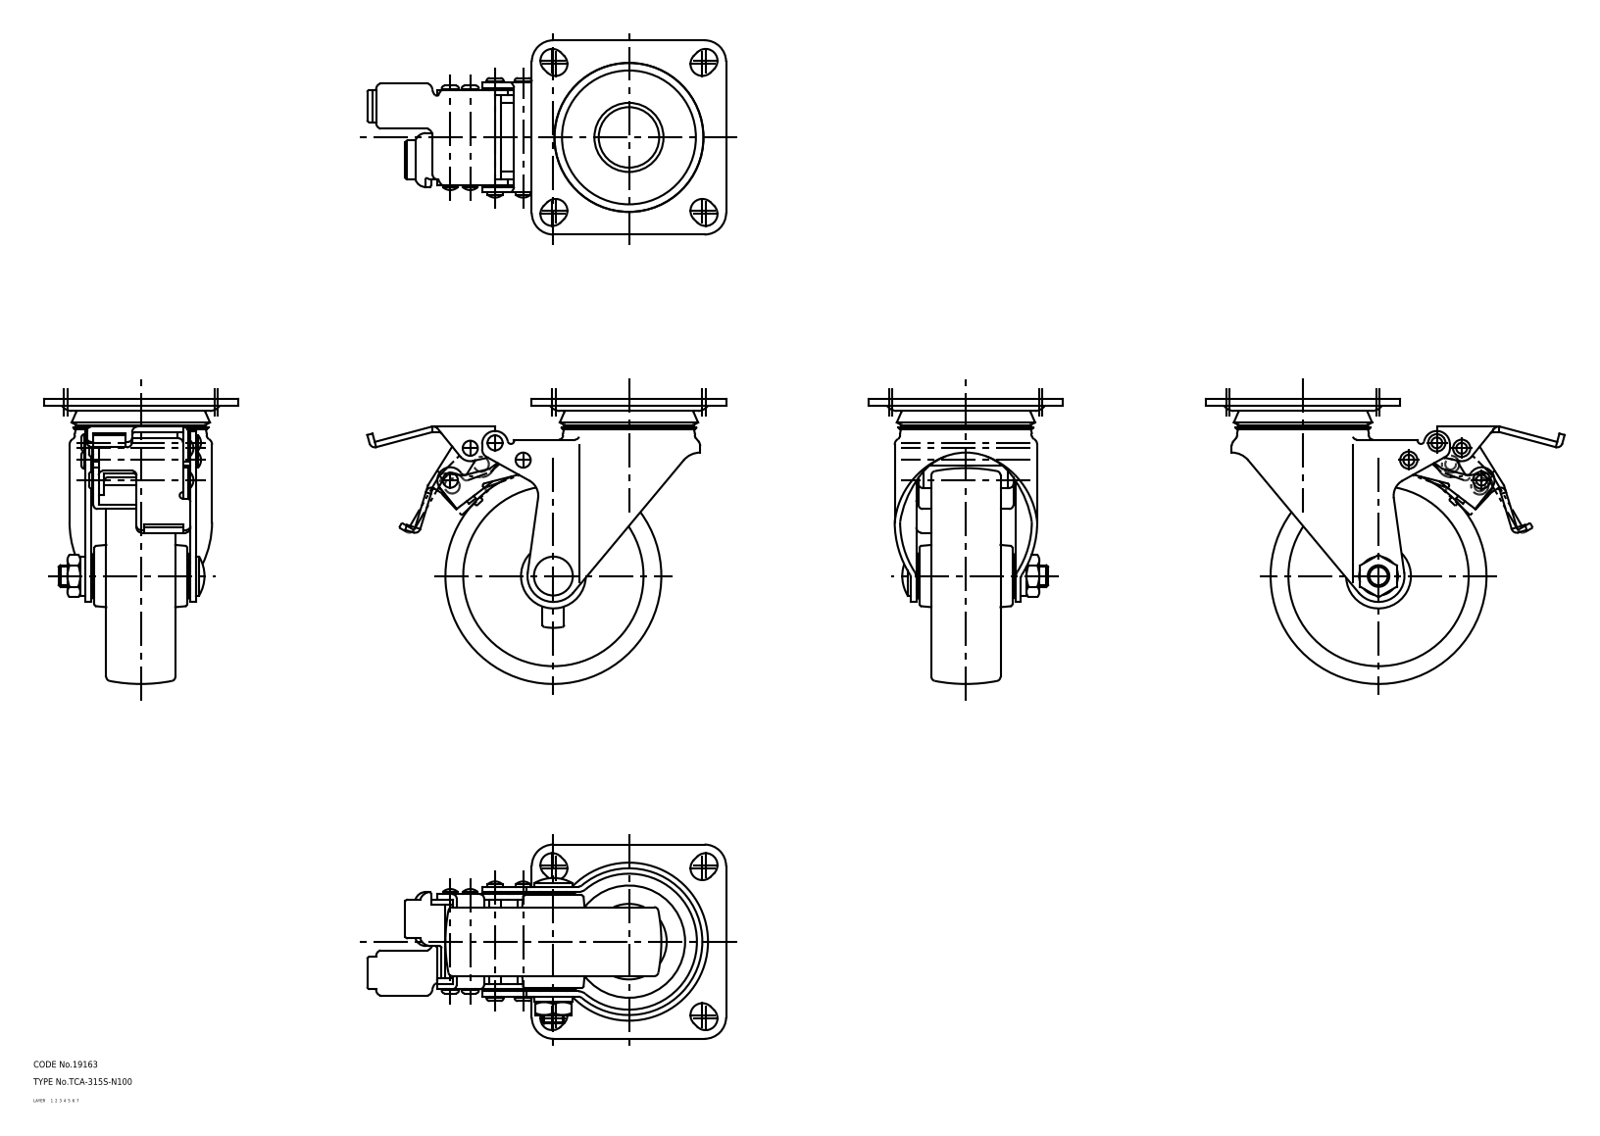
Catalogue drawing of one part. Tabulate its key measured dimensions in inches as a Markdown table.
| quantity | value |
| --- | --- |
| part name | 67138004; 67138017; 67138030; 67138043 (+2 more) |
| STEP written by | CADfix (AUTOMOTIVE_DESIGN) |
| units | inches |
| bodies | 6 solids, 462 faces (0 planar, 0 cylindrical, 462 other) |
| overall size | 6.543 × 5.197 × 3.543 |
| volume | 18.24 in³ |
| surface area | 159.5 in² |
